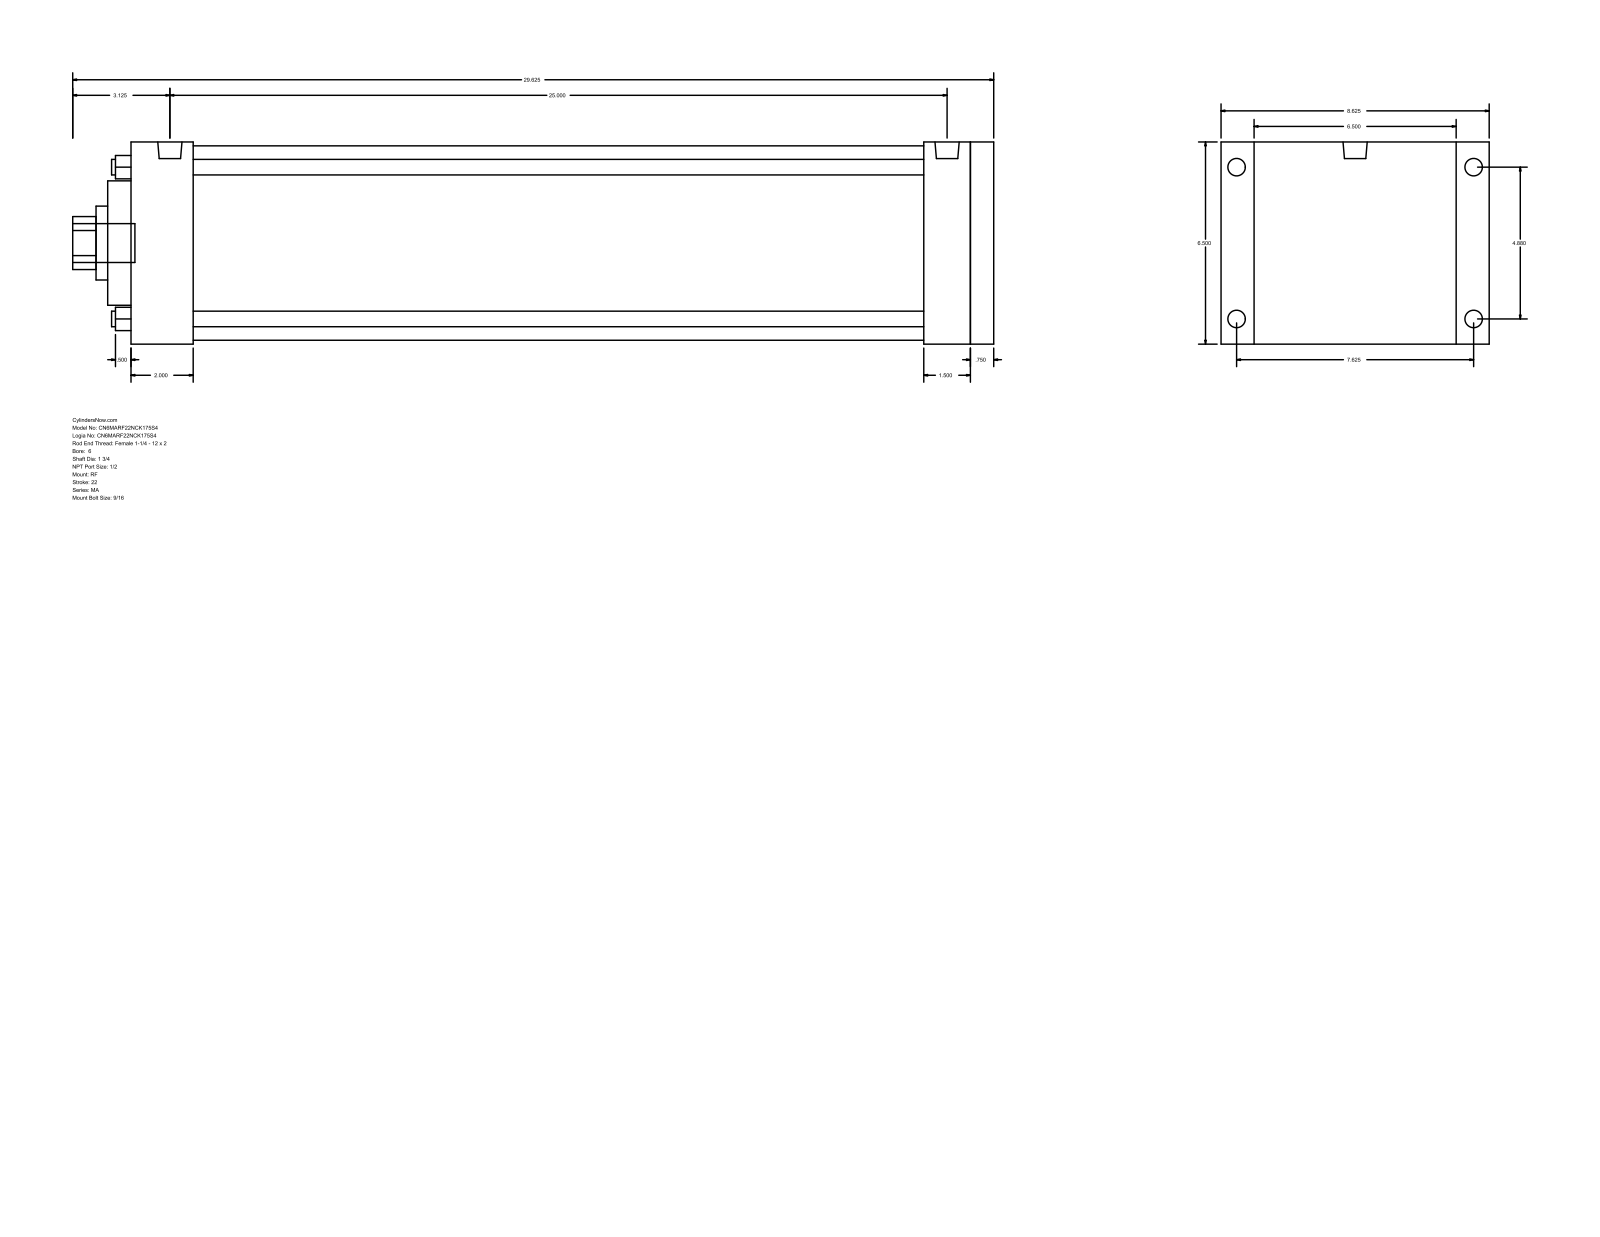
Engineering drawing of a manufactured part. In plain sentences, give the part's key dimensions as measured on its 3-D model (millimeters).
The part is named "MA_RF__0600_1.75". Its 3-D file was written by "GSSL Pune (CONFIG_CONTROL_DESIGN)". It is 0 solids with 94 faces: 65 planar, 29 cylindrical and 0 other. Overall it measures 752.48 by 219.07 by 165.1 millimeters. Round holes: 4 of diameter 12.7, 1 of diameter 44.45, 1 of diameter 60.33, 1 of diameter 101.6, 1 of diameter 158.75. Round bosses or shafts: 4 of diameter 17.46, 4 of diameter 14.29, 2 of diameter 19.77, 1 of diameter 31.75. Partial cylindrical surfaces (rounded edges, fillets, slot ends): 1 of radius 21.63. The main face-to-face distances are 165.1, 704.86, 685.8, 19.06, 19.05, 50.8, 635, 654.06, 647.71, 596.91. The hole center spacings are 87.65, 123.96, 175.31.
